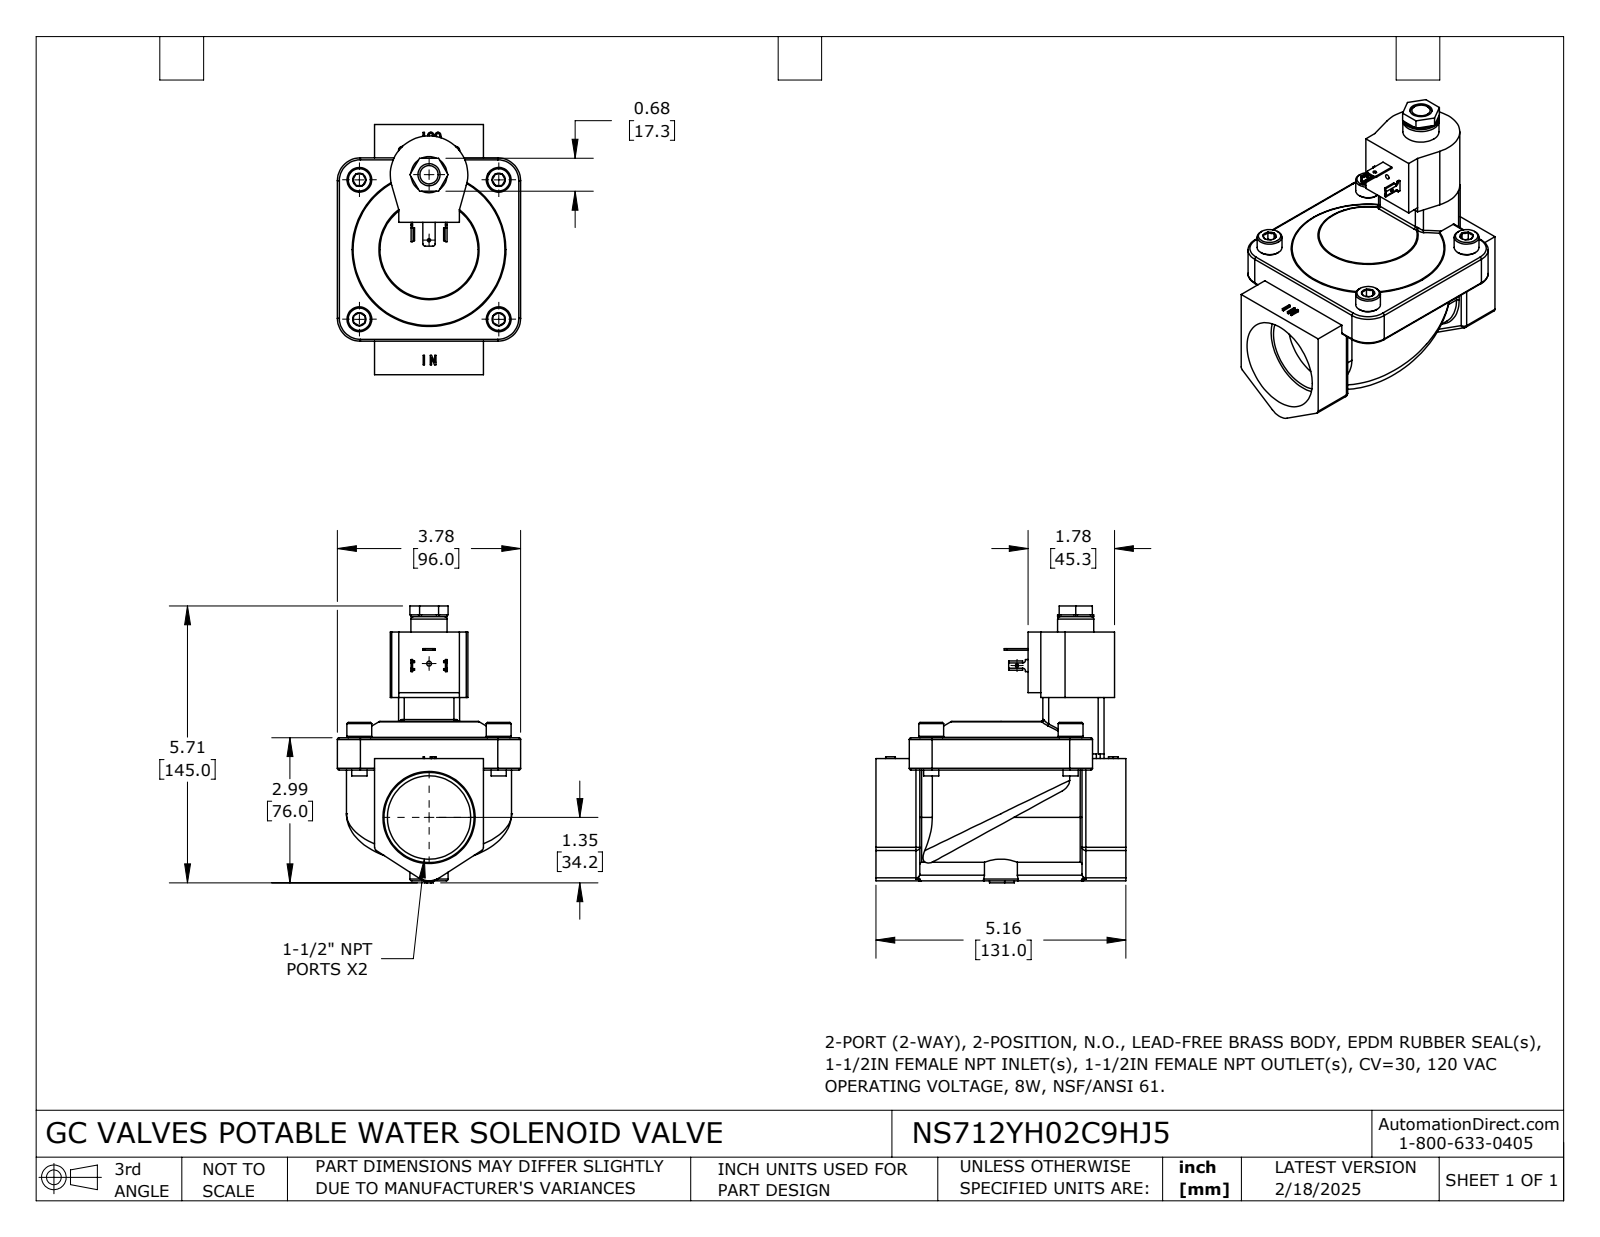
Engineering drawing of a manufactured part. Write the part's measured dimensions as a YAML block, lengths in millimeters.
part_name: "NS712YH02C9HJ5"
step_written_by: "SolidWorks 2024 (CONFIG_CONTROL_DESIGN)"
units: millimeters
bodies: {solids: 1, faces: 456, planar: 206, cylindrical: 120, other: 130}
overall_size: [145.01, 131, 96]
volume: 541187
surface_area: 71904
round_holes:
  - {diameter: 1.68, count: 1}
  - {diameter: 1.7, count: 1}
  - {diameter: 2.53, count: 1}
  - {diameter: 11.58, count: 1}
  - {diameter: 30.48, count: 1}
  - {diameter: 43.66, count: 1}
round_bosses_or_shafts:
  - {diameter: 13, count: 4}
  - {diameter: 8, count: 4}
  - {diameter: 18.95, count: 1}
partial_cylinders:
  - {radius: 2, count: 14}
  - {radius: 1, count: 13}
  - {radius: 3, count: 6}
  - {radius: 0.15, count: 4}
  - {radius: 1.04, count: 4}
  - {radius: 12, count: 4}
  - {radius: 0.2, count: 2}
  - {radius: 1.27, count: 2}
face_to_face_distances: [19.5, 11, 32, 6, 76.5, 8.5, 96, 17, 25.5, 57]
hole_center_spacings: [34.29, 80.56]
